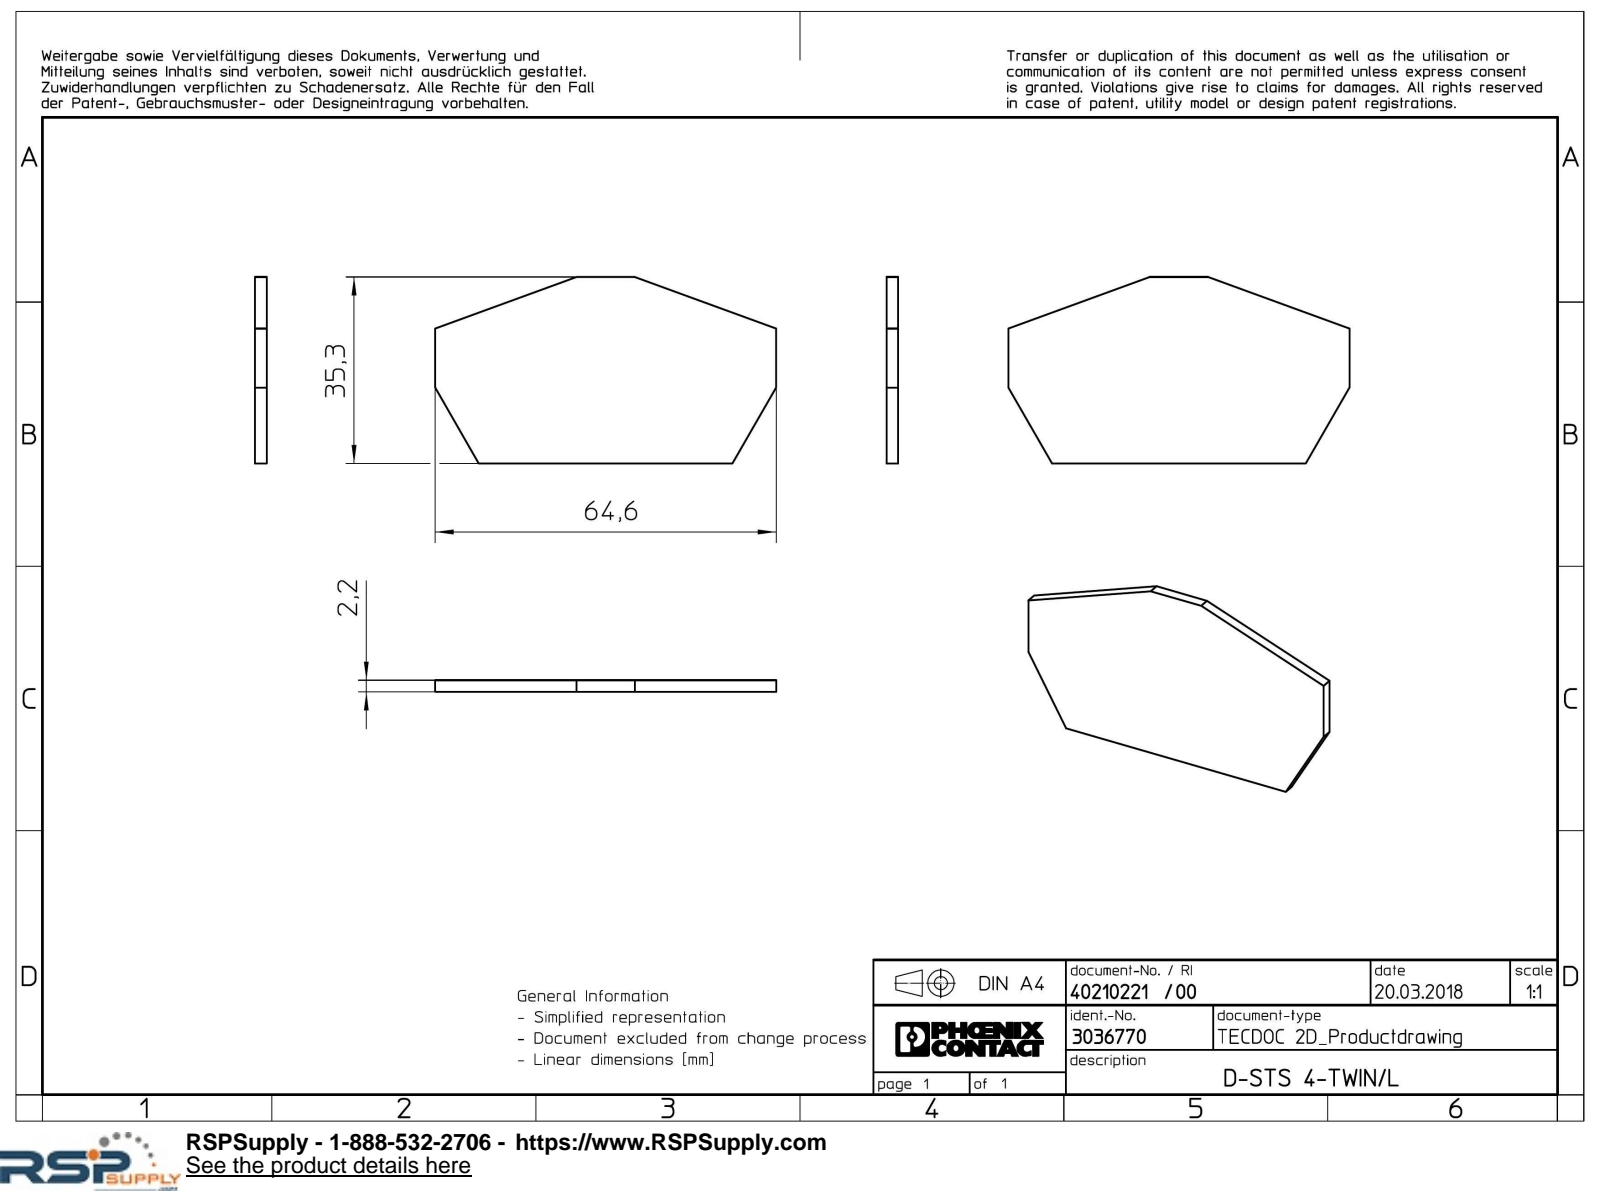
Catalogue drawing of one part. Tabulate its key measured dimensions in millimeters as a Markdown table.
| quantity | value |
| --- | --- |
| part name | d_sts4_twin_l_select |
| STEP written by | Creo Elements/Direct Modeling 18.1I 14-Aug-2016 (C) Parametric Technology GmbH (AUTOMOTIVE_DESIGN) |
| units | millimeters |
| bodies | 1 solid, 10 faces (10 planar, 0 cylindrical, 0 other) |
| overall size | 64.6 × 35.3 × 2.2 |
| volume | 4 181 mm³ |
| surface area | 4 178 mm² |
| main face-to-face distances | 2.2, 64.6, 35.3 |
